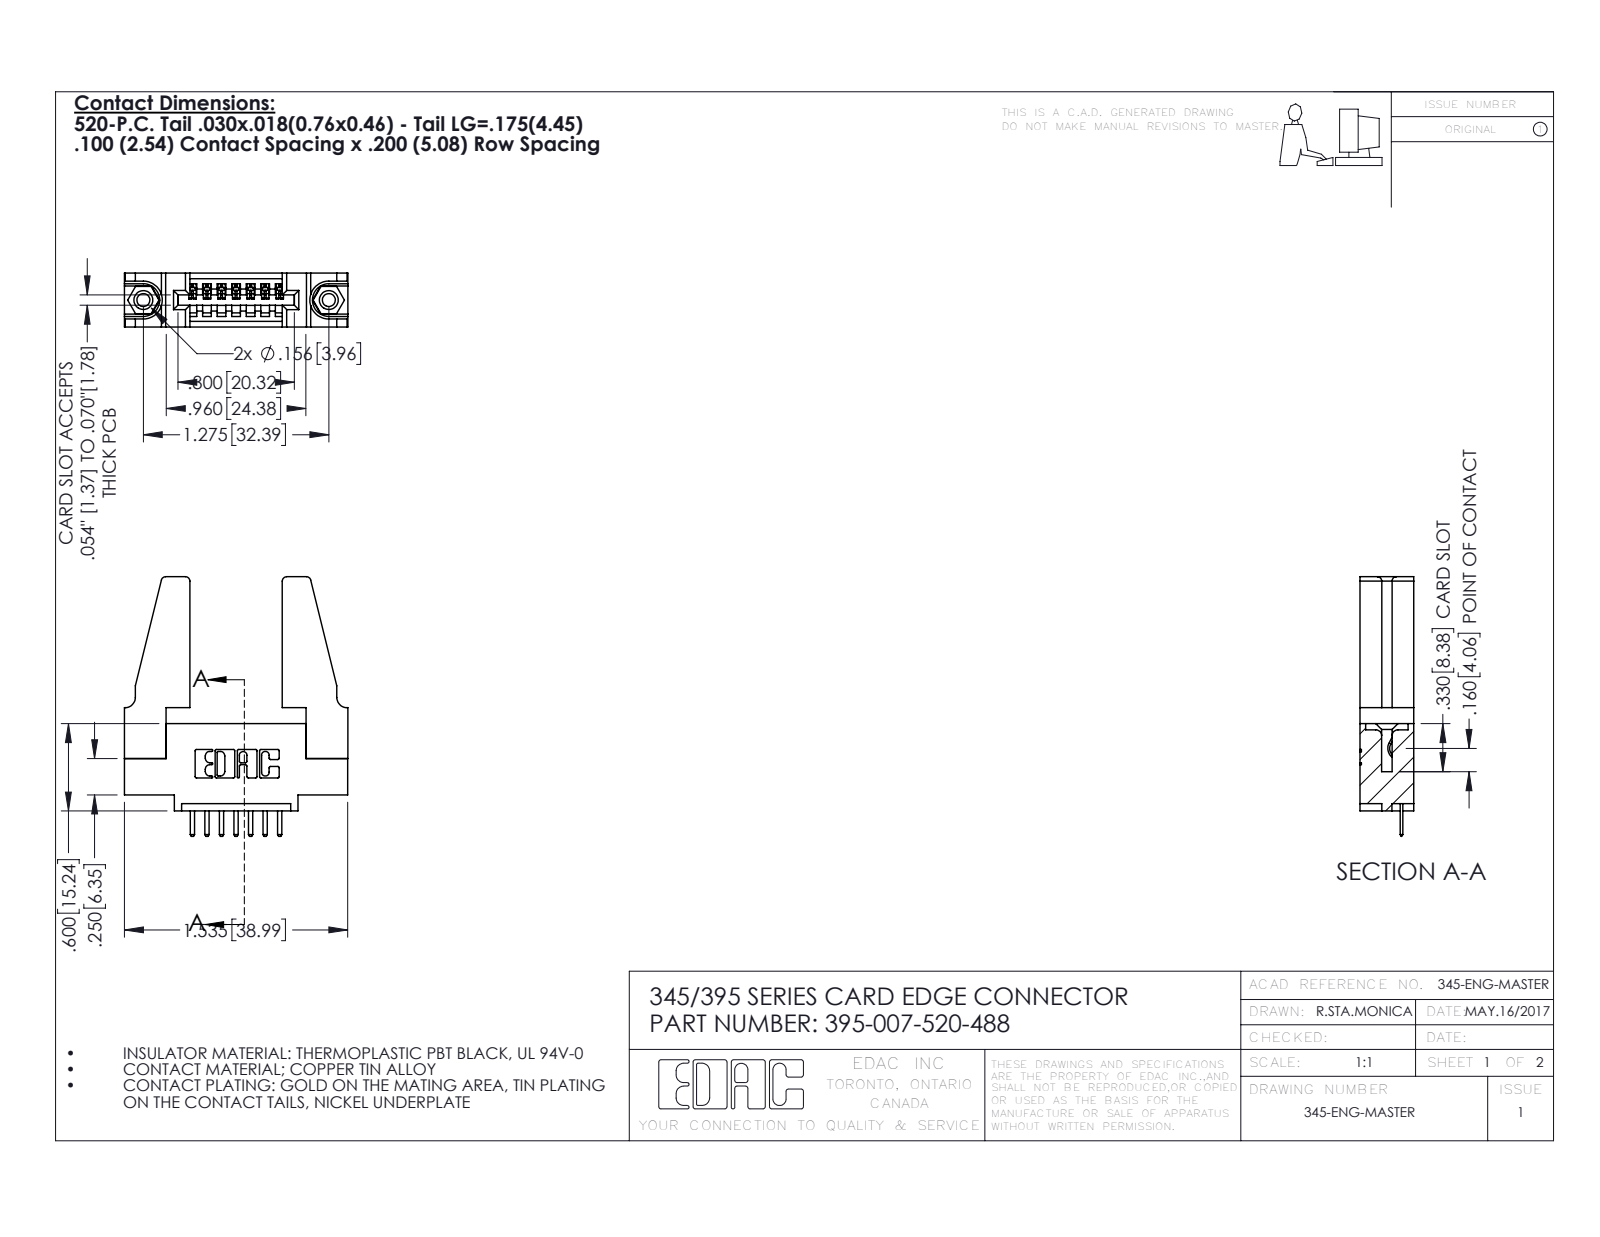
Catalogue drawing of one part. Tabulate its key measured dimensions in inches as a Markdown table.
| quantity | value |
| --- | --- |
| part name | 345-250-001_345-250-001-102; 345-292-001_345-293-120; 395-007-520-488; 345 Part_0.110 Offset - 0.156 Dia-TH (+1 more) |
| STEP written by | SolidWorks 2016 (CONFIG_CONTROL_DESIGN) |
| units | inches |
| bodies | 12 solids, 688 faces (450 planar, 222 cylindrical, 16 other) |
| overall size | 1.785 × 1.536 × 0.37 |
| volume | 0.401 in³ |
| surface area | 10.99 in² |
| round holes (diameter × count) | 0.089 × 2, 0.125 × 2, 0.156 × 2, 0.064 × 1 |
| round bosses / shafts (diameter × count) | 0.155 × 2 |
| partial cylindrical surfaces (radius × count) | 0.01 × 22, 0.01 × 16, 0.006 × 14, 0.03 × 8, 0.007 × 6, 0.031 × 6, 0.026 × 3, 0.031 × 2 |
| main face-to-face distances | 0.37, 0.072, 0.298, 0.2, 0.148, 0.15, 0.6, 0.098, 0.272, 0.025 |
| hole center spacings | 0.27, 1.045, 1.275 |
